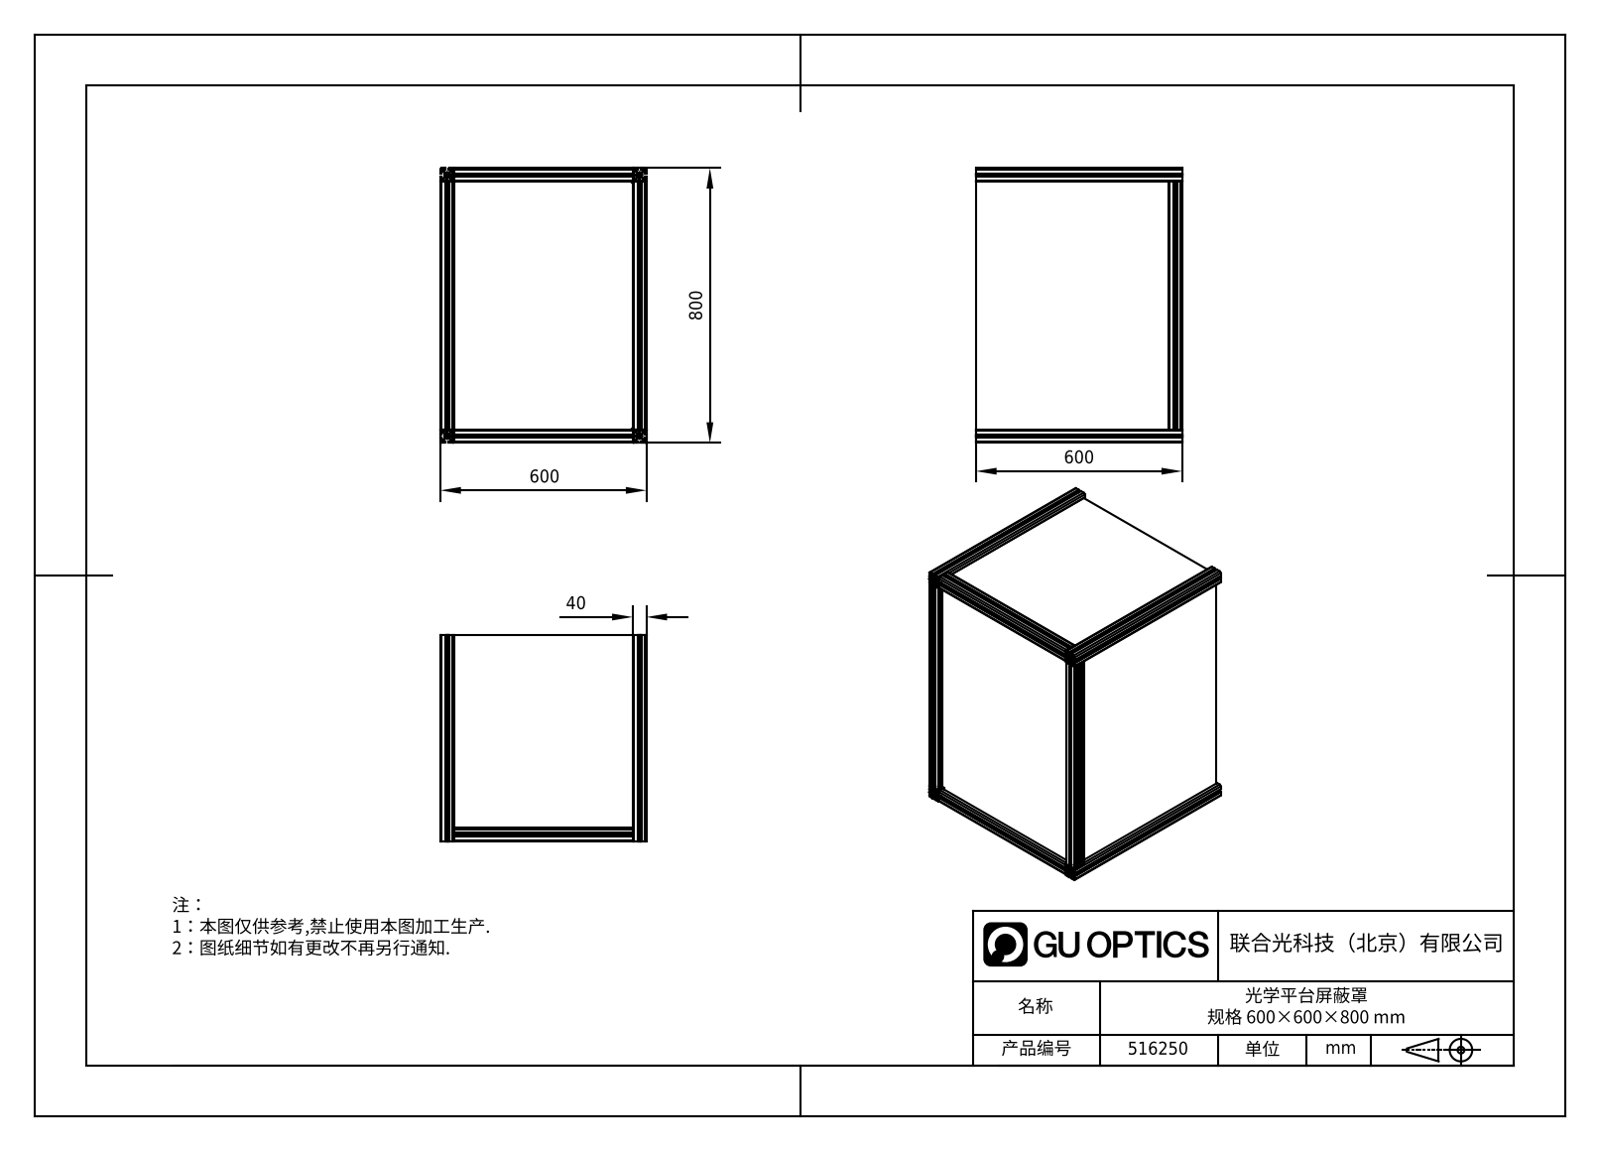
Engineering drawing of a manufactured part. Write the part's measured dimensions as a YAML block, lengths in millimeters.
part_name: "型材板3; 型材520; 型材600-600-800; 型材板2 (+3 more)"
step_written_by: "SolidWorks 2020 (AUTOMOTIVE_DESIGN)"
units: millimeters
bodies: {solids: 13, faces: 1230, planar: 950, cylindrical: 280, other: 0}
overall_size: [800, 600, 600]
volume: 6679000
surface_area: 6191000
partial_cylinders:
  - {radius: 0.5, count: 64}
  - {radius: 1, count: 64}
  - {radius: 0.75, count: 32}
  - {radius: 2.5, count: 32}
  - {radius: 4.5, count: 32}
  - {radius: 3.4, count: 8}
face_to_face_distances: [2, 560, 760, 19, 562, 558, 21, 762, 758, 8.2]
